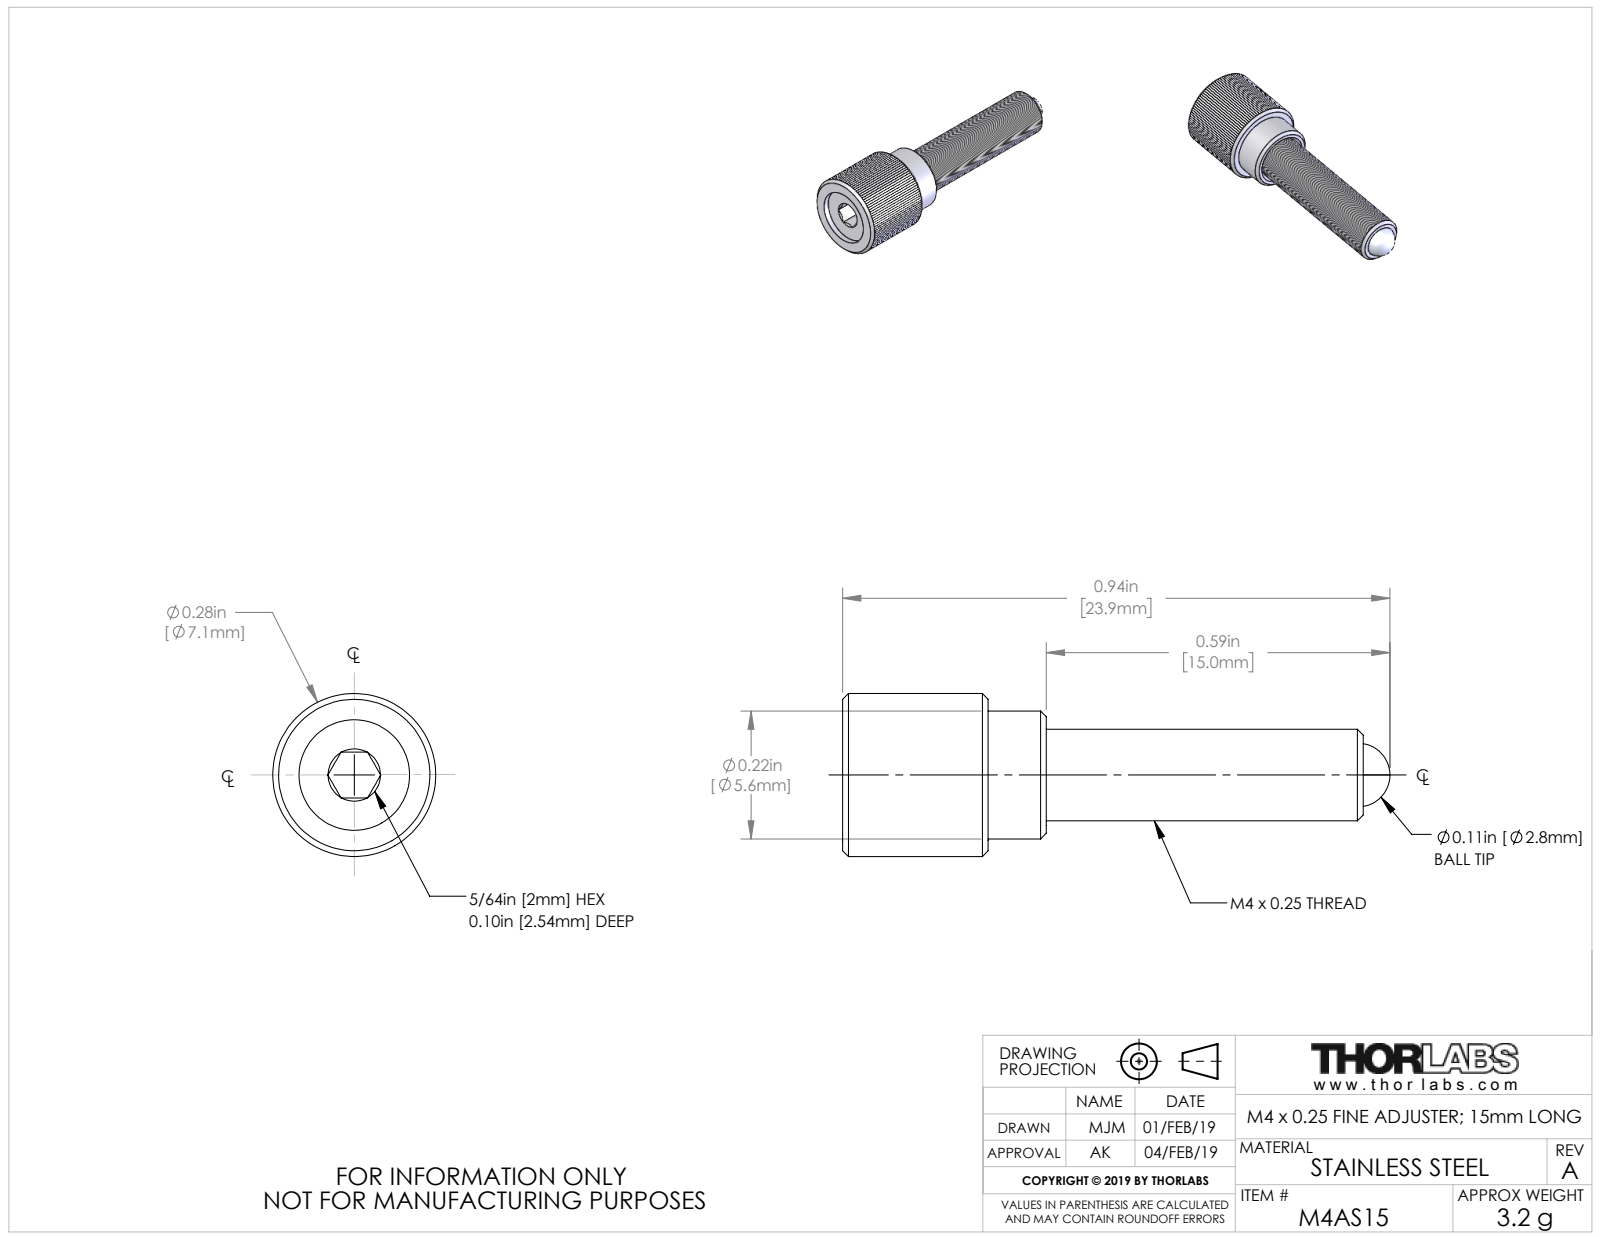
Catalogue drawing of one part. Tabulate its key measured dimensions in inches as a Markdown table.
| quantity | value |
| --- | --- |
| part name | TTN175598-E0W |
| STEP written by | SolidWorks 2018 (AUTOMOTIVE_DESIGN) |
| units | inches |
| bodies | 3 solids, 50 faces (14 planar, 12 cylindrical, 24 other) |
| overall size | 0.941 × 0.28 × 0.28 |
| volume | 0.028 in³ |
| surface area | 0.964 in² |
| round holes (diameter × count) | 0.11 × 1, 0.157 × 1, 0.19 × 1 |
| round bosses / shafts (diameter × count) | 0.28 × 1, 0.22 × 1, 0.157 × 1 |
| main face-to-face distances | 0.1, 0.13, 0.02, 0.23, 0.15, 0.25, 0.057, 0.043, 0.173, 0.193 |
